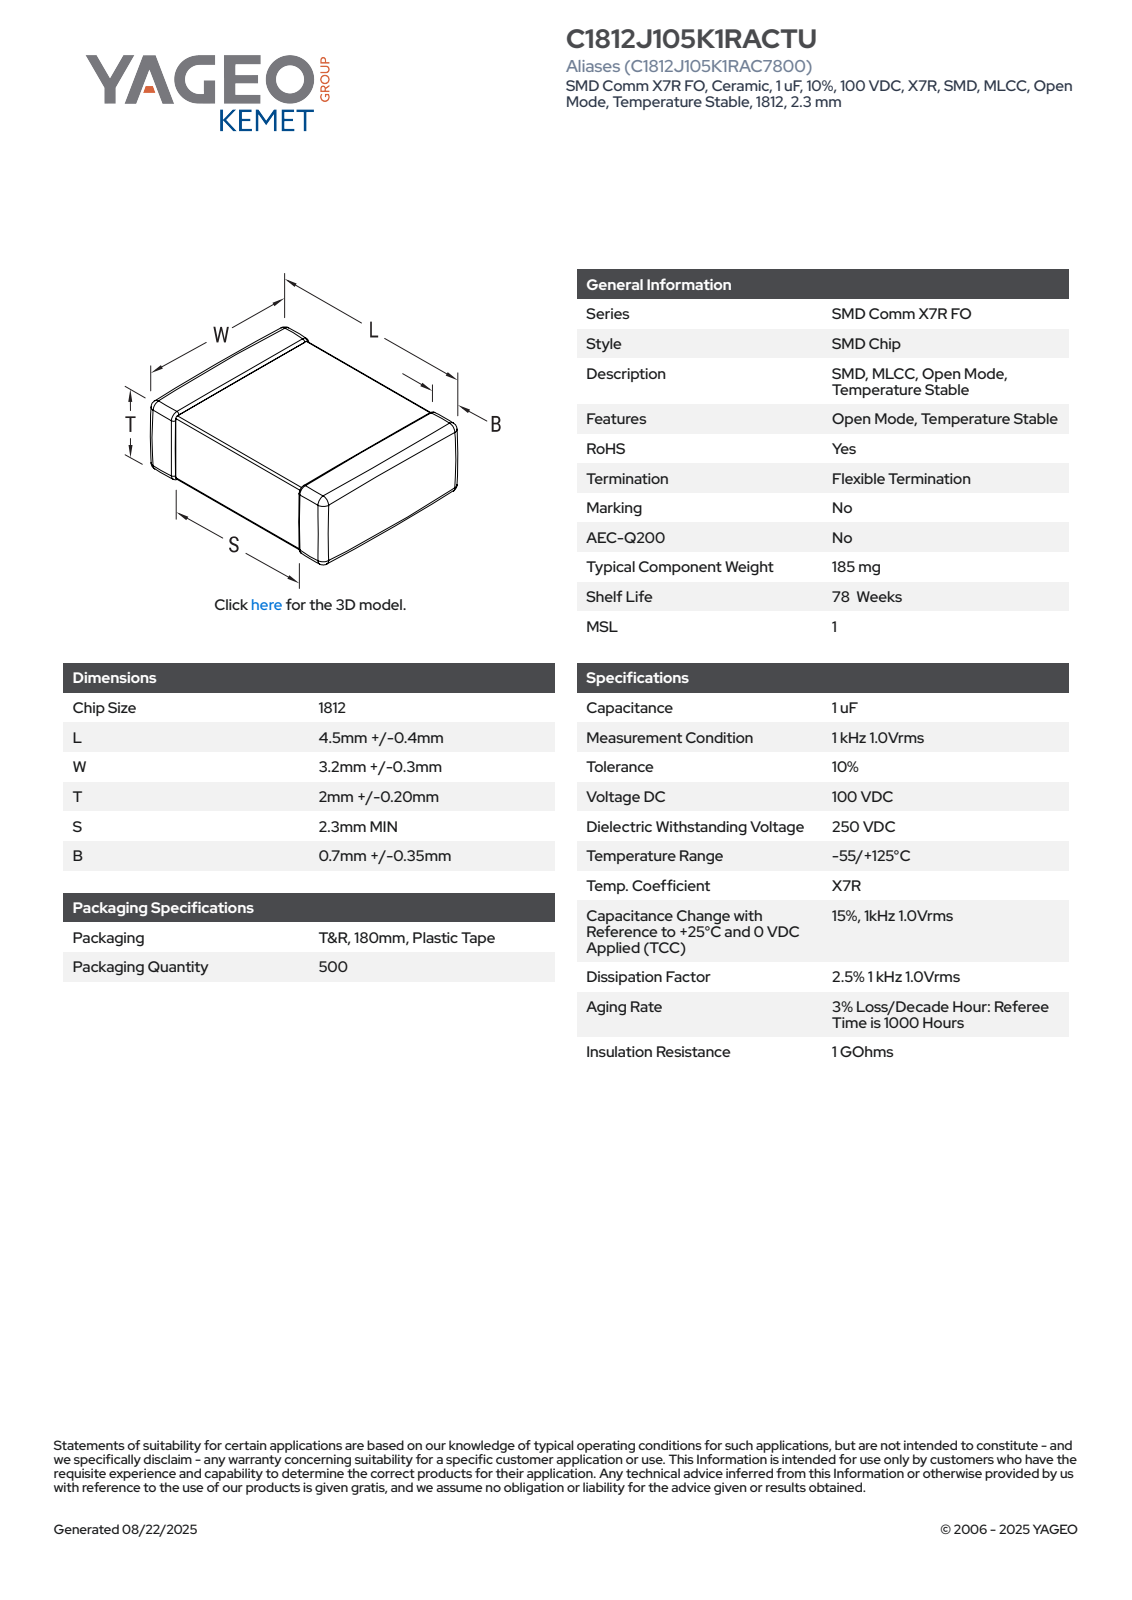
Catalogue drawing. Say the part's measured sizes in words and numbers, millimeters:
The part is named "CCS_CCSTD_1812_L4.9W3.5T2.2B0.7". Its 3-D file was written by "SolidWorks 2021 (AUTOMOTIVE_DESIGN)". It is 4 solids with 121 faces: 71 planar, 34 cylindrical and 16 other. Overall it measures 4.9 by 3.5 by 2.2 millimeters. Its volume is 35 cubic millimeters and its surface area 71 square millimeters. The main face-to-face distances are 2.13, 2.06, 3.43, 4.9, 2.2, 3.36, 3.5, 0.52, 2.25, 2.77.
